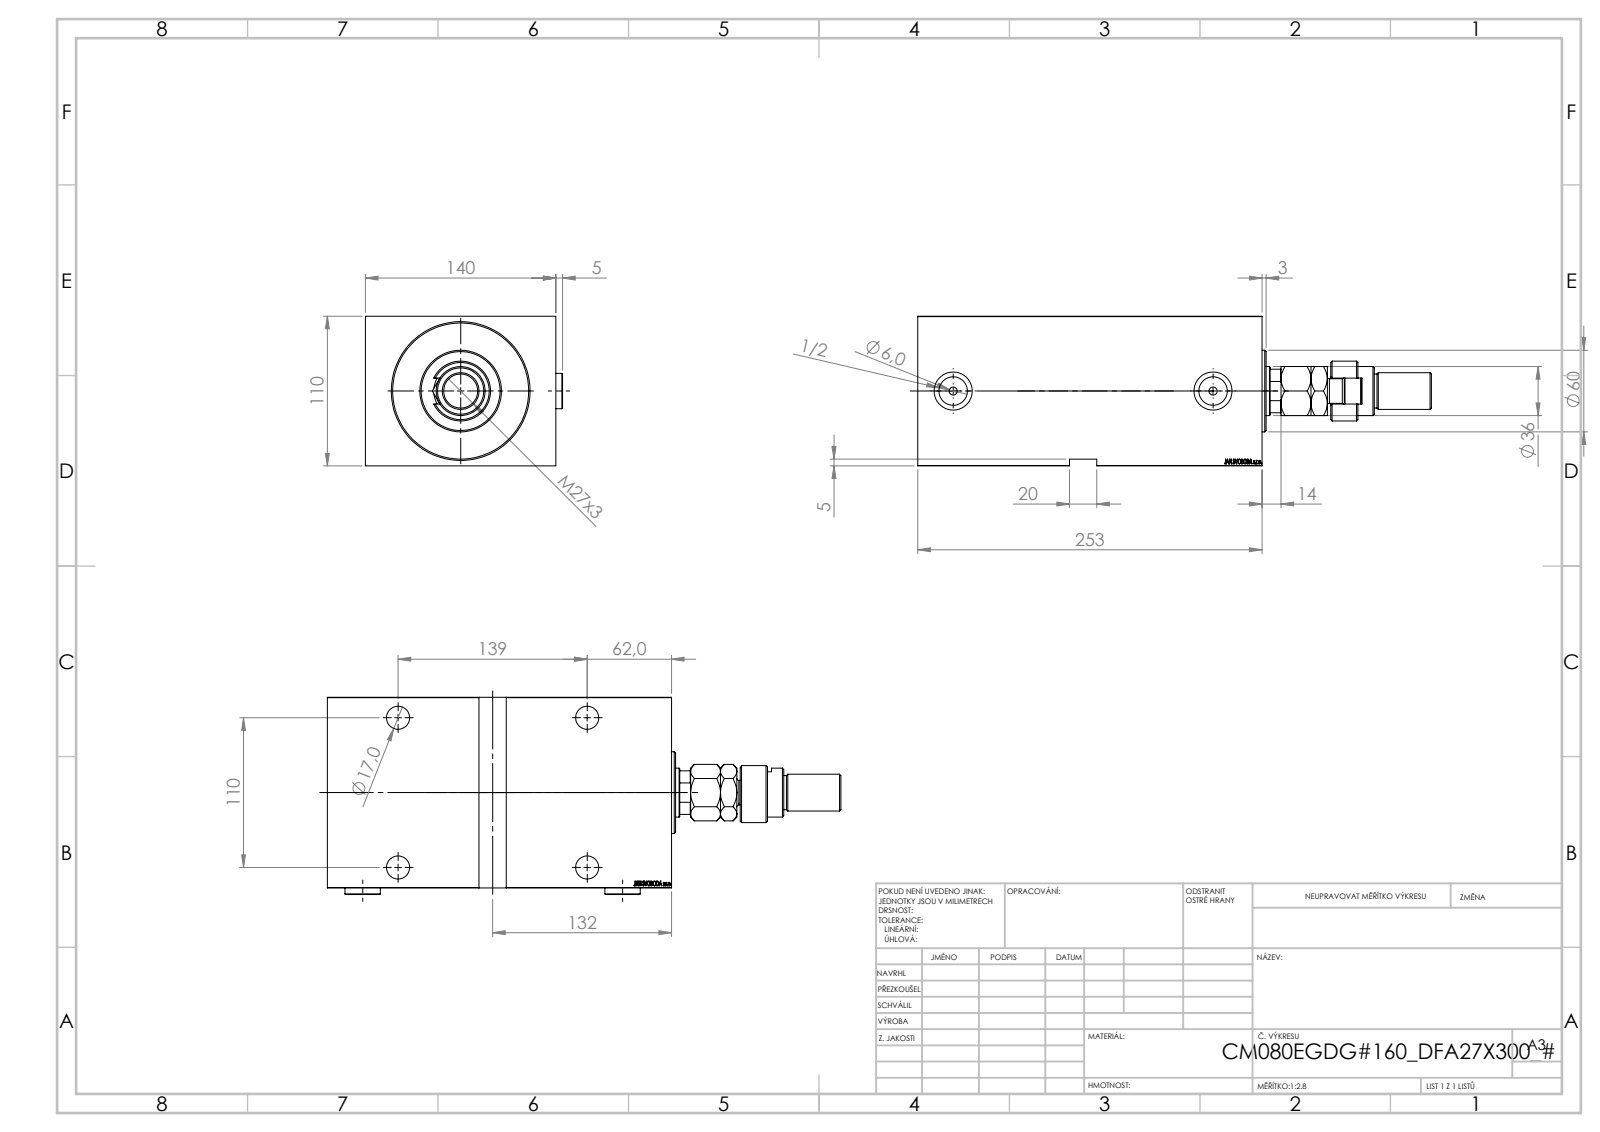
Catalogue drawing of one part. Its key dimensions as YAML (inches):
part_name: "MFA; V450CM_VC_B; Zatka_OIL_PORT; V450CM_E_VCP (+2 more)"
step_written_by: "SolidWorks 2019 (CONFIG_CONTROL_DESIGN)"
units: inches
bodies: {solids: 7, faces: 997, planar: 474, cylindrical: 81, other: 442}
overall_size: [14.862, 5.705, 4.331]
volume: 195.9
surface_area: 525.5
round_holes:
  - {diameter: 0.669, count: 4}
  - {diameter: 0.984, count: 4}
  - {diameter: 0.236, count: 2}
  - {diameter: 0.825, count: 2}
  - {diameter: 1.102, count: 2}
  - {diameter: 1.004, count: 1}
  - {diameter: 1.555, count: 1}
  - {diameter: 3.15, count: 1}
  - {diameter: 3.937, count: 1}
round_bosses_or_shafts:
  - {diameter: 1.024, count: 2}
  - {diameter: 3.228, count: 1}
  - {diameter: 2.362, count: 1}
  - {diameter: 1.732, count: 1}
  - {diameter: 1.417, count: 1}
  - {diameter: 1.102, count: 1}
  - {diameter: 1.063, count: 1}
  - {diameter: 0.984, count: 1}
partial_cylinders:
  - {radius: 0.374, count: 1}
  - {radius: 0.591, count: 1}
  - {radius: 0.689, count: 1}
face_to_face_distances: [4.331, 5.512, 9.961, 0.827, 9.134, 0.197, 9.764, 8.937, 3.11, 9.307]
hole_center_spacings: [4.331, 5.472, 6.979, 7.52]
